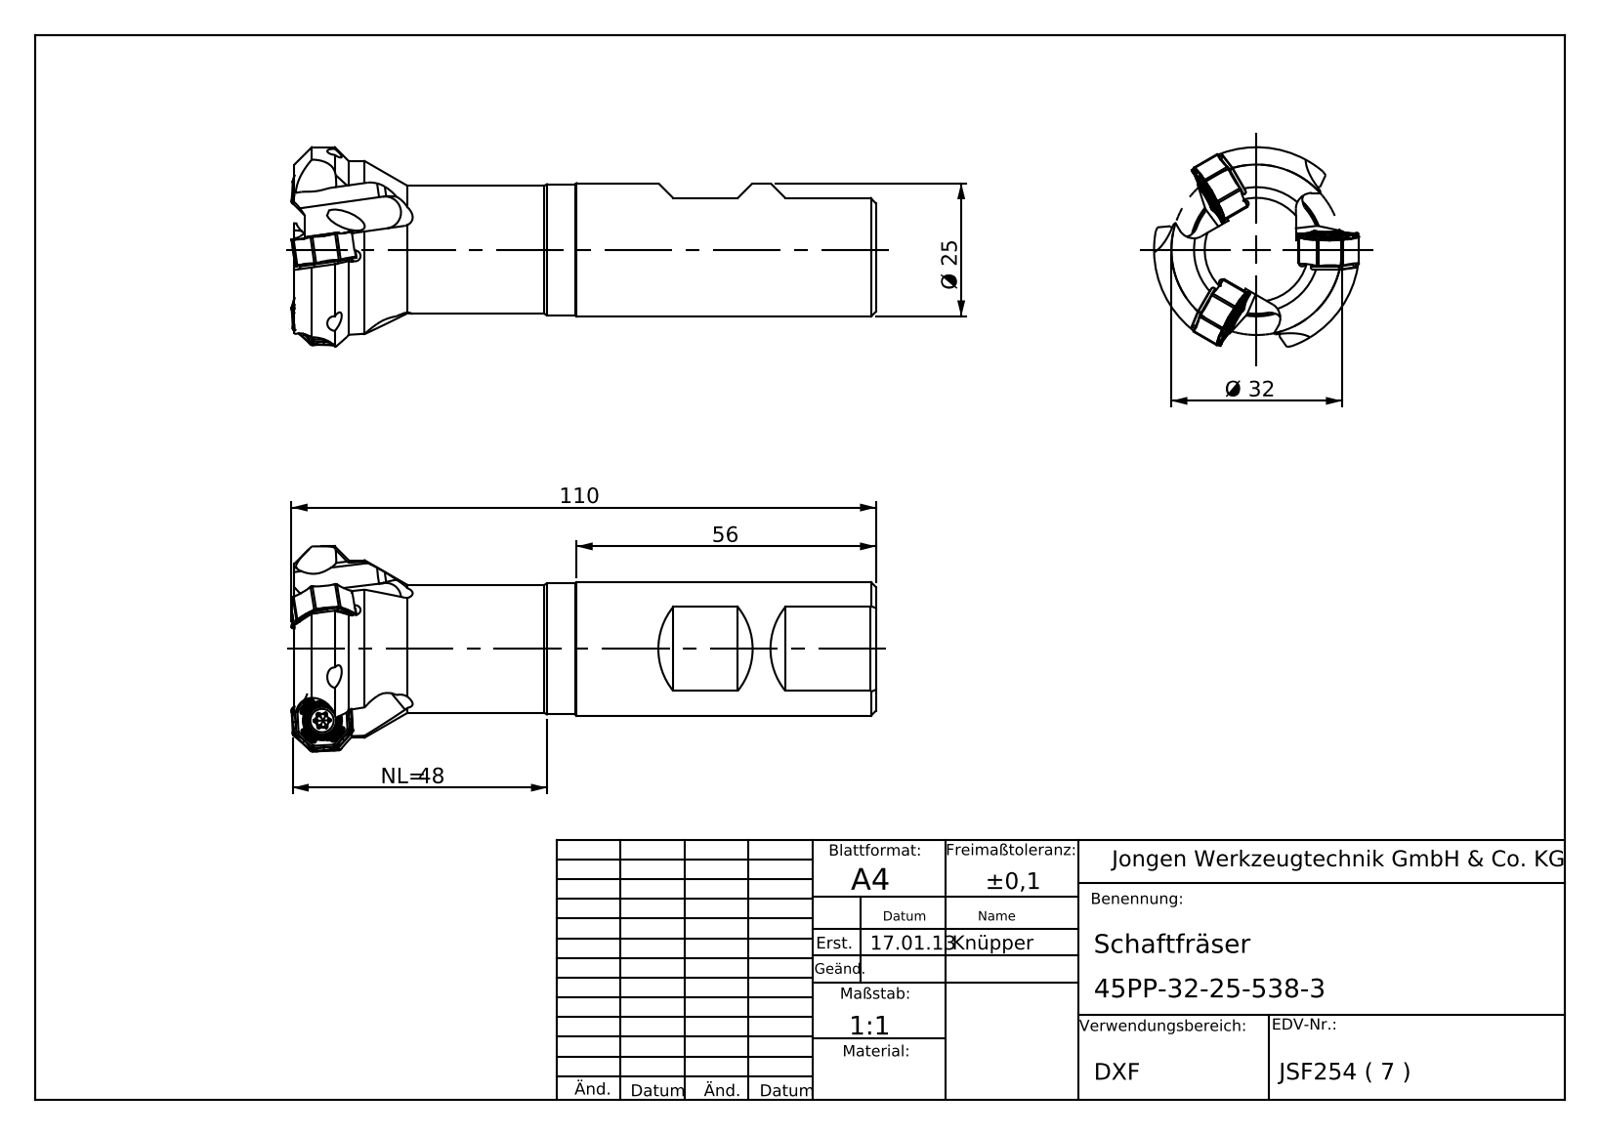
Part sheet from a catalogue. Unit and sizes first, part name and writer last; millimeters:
Units: millimetres
Overall size (bounding box): 110.04 × 39.61 × 39.61
Round holes (diameter × count): ⌀3 ×3, ⌀6.5 ×1
Round bosses / shafts (diameter × count): ⌀25 ×1, ⌀24.6 ×1, ⌀24 ×1
Partial cylindrical surfaces — rounded edges, fillets, slot ends (radius × count): R0.5 ×3, R0.64 ×3, R1 ×3, R1.25 ×3, R3 ×3, R16.65 ×1
Main face-to-face distances: 107.15, 14.88, 0.48, 11.31, 26.19, 0.47, 5.3, 5.32, 14.31, 0.31
Volume: 55 997 mm³ · Surface area: 13 764 mm²
Bodies: 1 solid, 137 faces (56 planar, 47 cylindrical, 34 other)
Part name (STEP PRODUCT): 45PP-32-25-538-3
STEP written by: SolidWorks 2013 (AUTOMOTIVE_DESIGN)
